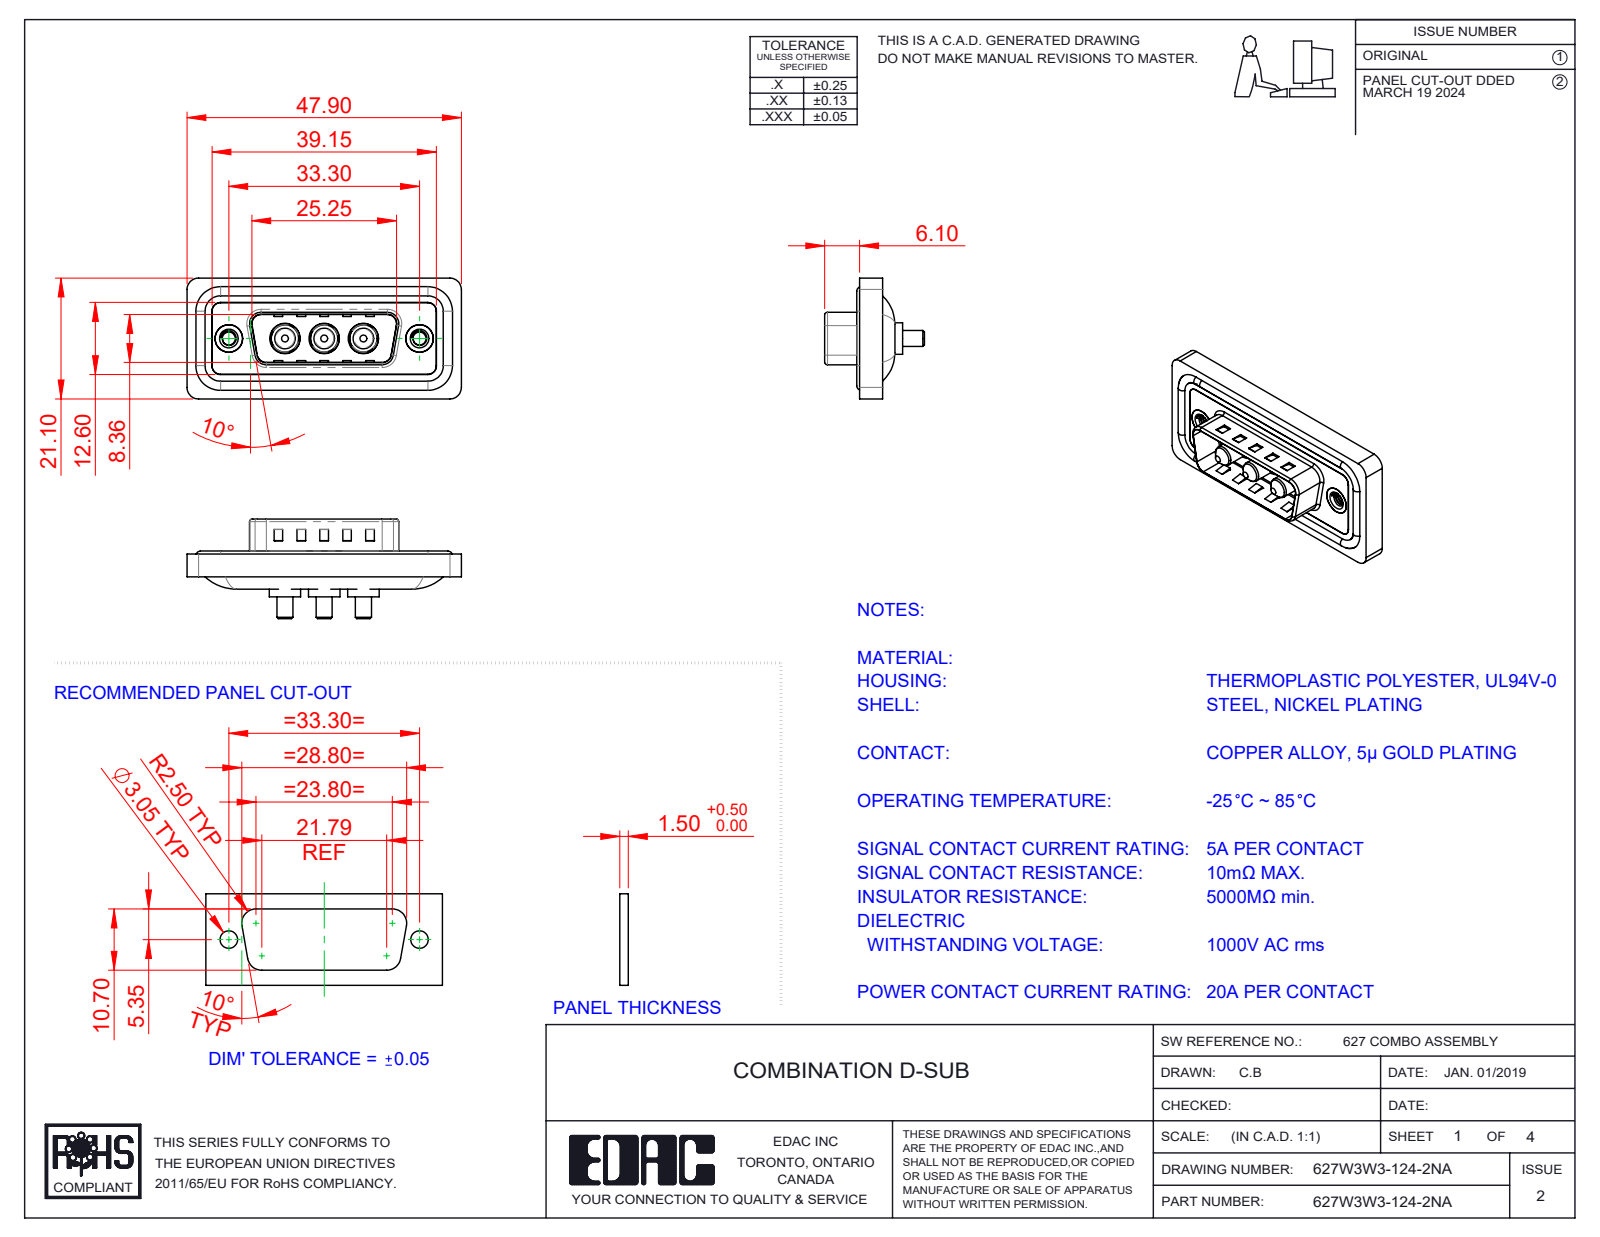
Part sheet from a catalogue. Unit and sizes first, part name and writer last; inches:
Units: inches
Overall size (bounding box): 1.886 × 0.831 × 0.685
Round holes (diameter × count): ⌀0.191 ×3, ⌀0.209 ×3, ⌀0.089 ×2, ⌀0.157 ×2, ⌀0.189 ×2, ⌀0.197 ×2
Round bosses / shafts (diameter × count): ⌀0.063 ×4, ⌀0.217 ×3, ⌀0.205 ×3, ⌀0.187 ×3, ⌀0.148 ×3, ⌀0.142 ×3, ⌀0.11 ×3, ⌀0.193 ×2
Partial cylindrical surfaces — rounded edges, fillets, slot ends (radius × count): R0.059 ×26, R0.079 ×20, R0.02 ×8, R0.063 ×8, R0.01 ×4, R0.024 ×4, R0.026 ×4, R0.035 ×4
Main face-to-face distances: 0.016, 0.043, 0.059, 0.02, 0.063, 0.122, 0.114, 0.157, 0.032, 0.377
Hole centre spacings: 0.27, 0.386, 0.656, 0.925, 0.539, 1.311
Volume: 0.341 in³ · Surface area: 13.56 in²
Bodies: 13 solids, 562 faces (207 planar, 243 cylindrical, 112 other)
Part name (STEP PRODUCT): 627Combo Shell Rear_15 Contacts; 627Combo Threaded Rivet_A; 627Combo Shell Front_15 Contacts; 627W3W3-124-2NA (+3 more)
STEP written by: SolidWorks 2023 (CONFIG_CONTROL_DESIGN)
